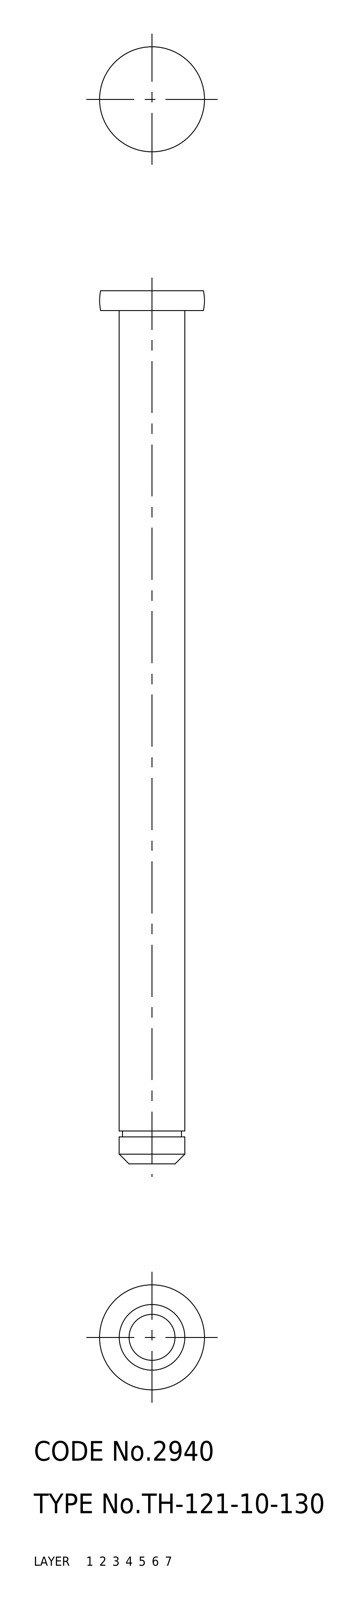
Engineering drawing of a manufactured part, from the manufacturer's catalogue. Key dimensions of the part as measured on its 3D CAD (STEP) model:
Part name (STEP PRODUCT): shaft; TH_121_10_130
STEP written by: SolidWorks 2015 (AUTOMOTIVE_DESIGN)
Units: millimetres
Bodies: 1 solid, 15 faces (5 planar, 6 cylindrical, 4 other)
Overall size (bounding box): 133 × 16 × 16
Volume: 10 760 mm³ · Surface area: 4 617 mm²
Round bosses / shafts (diameter × count): ⌀10 ×1, ⌀9 ×1
Main face-to-face distances: 3, 130, 133, 5, 125, 128, 4.1, 0.9, 125.9, 128.9
